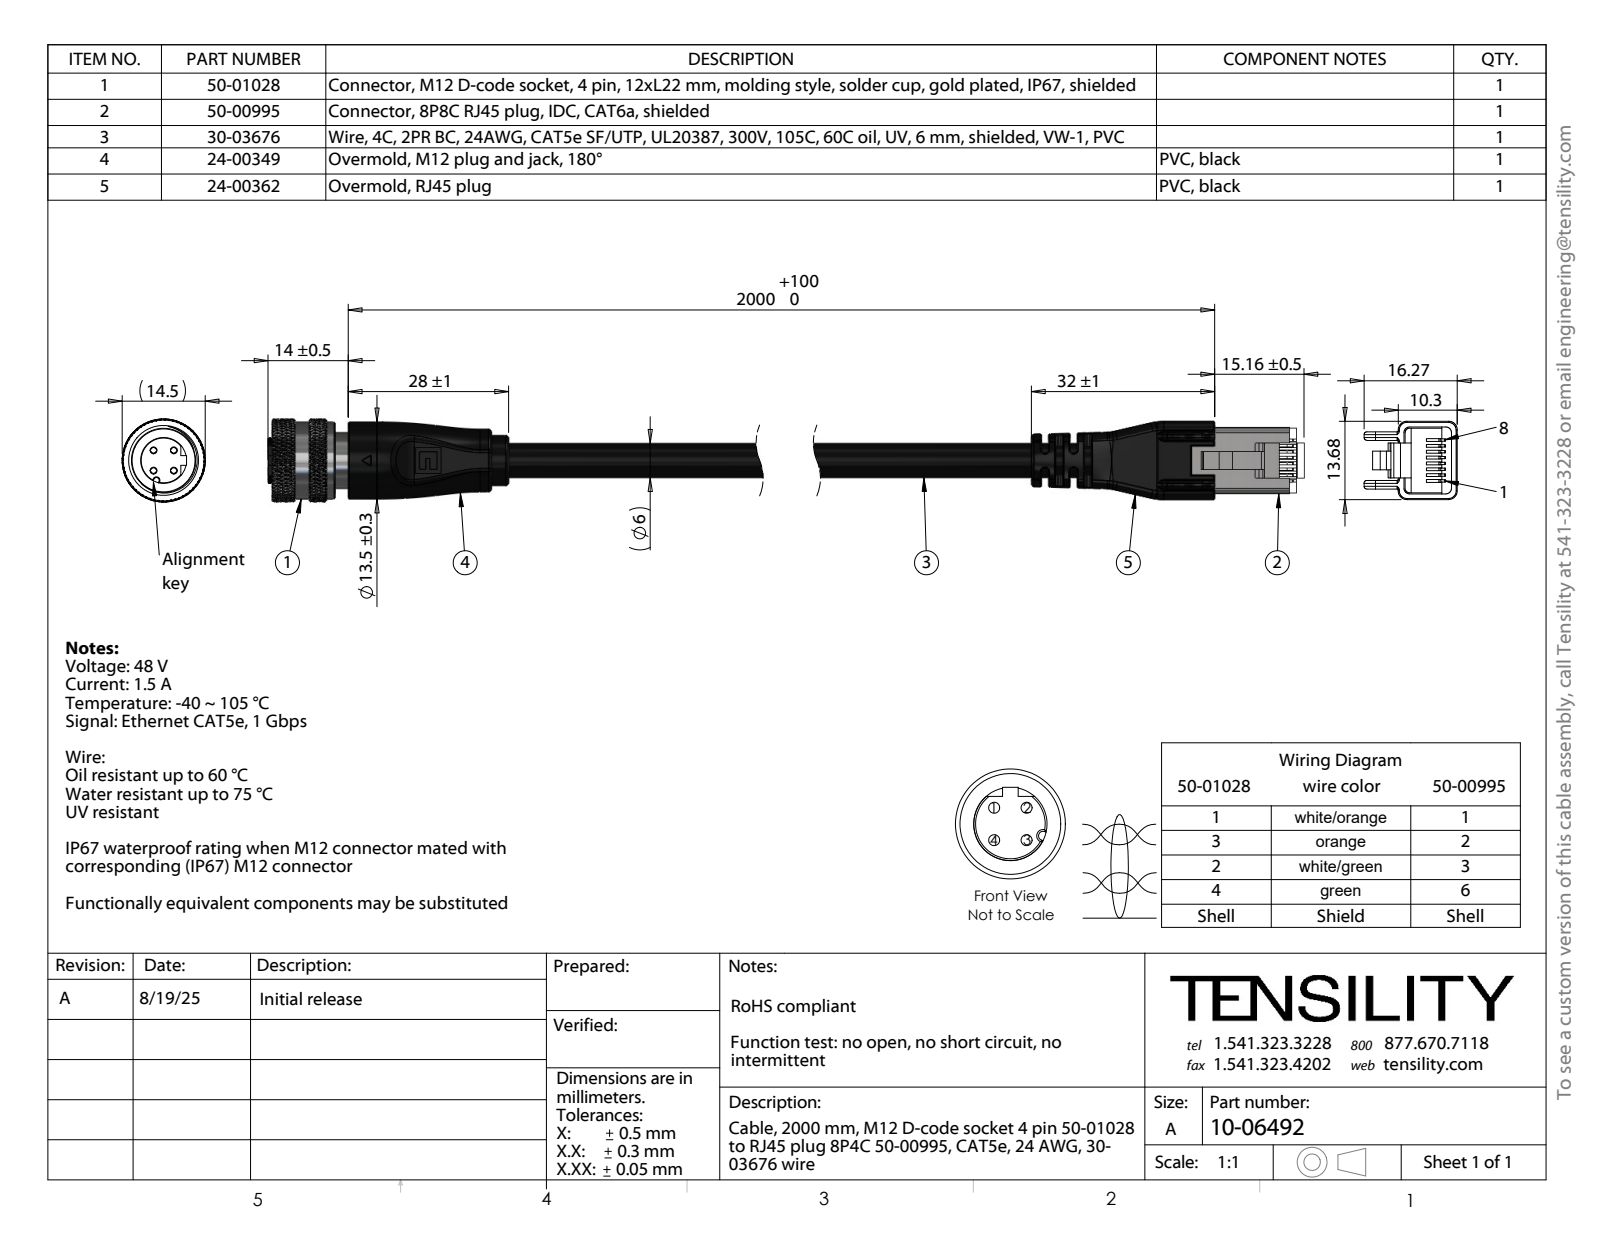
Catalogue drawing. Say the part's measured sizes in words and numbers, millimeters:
The part is named "24-00349_Mexico; 50-01028-05_默认; 50-00995; 50-01028_默认 (+7 more)". Its 3-D file was written by "SolidWorks 2025 (CONFIG_CONTROL_DESIGN)". It is 55 solids with 3967 faces: 546 planar, 928 cylindrical and 2493 other. Overall it measures 229.11 by 18.37 by 14.5 millimeters. Its volume is 14 248 cubic millimeters and its surface area 29 704 square millimeters. Round holes: 28 of diameter 0.2, 4 of diameter 1.05, 4 of diameter 1.1, 4 of diameter 1.2, 1 of diameter 3.16, 1 of diameter 3.21, 1 of diameter 3.56, 1 of diameter 9, 1 of diameter 10, 1 of diameter 11.2. Round bosses or shafts: 4 of diameter 1.6, 4 of diameter 1.5, 1 of diameter 13.5, 1 of diameter 11, 1 of diameter 10.6, 1 of diameter 10.5, 1 of diameter 9.8, 1 of diameter 9.7. Partial cylindrical surfaces (rounded edges, fillets, slot ends): 11 of radius 0.2, 10 of radius 0.1, 10 of radius 0.5, 10 of radius 1.5, 8 of radius 0.62, 6 of radius 0.4, 5 of radius 1, 4 of radius 10. The main face-to-face distances are 1.25, 1, 2.5, 3.75, 9.3, 5, 1.5, 199.5, 12.68, 8.5. The hole center spacings are 1.91, 0.36, 2.09, 1.06, 0.89, 1.08, 1.24, 1.8.
